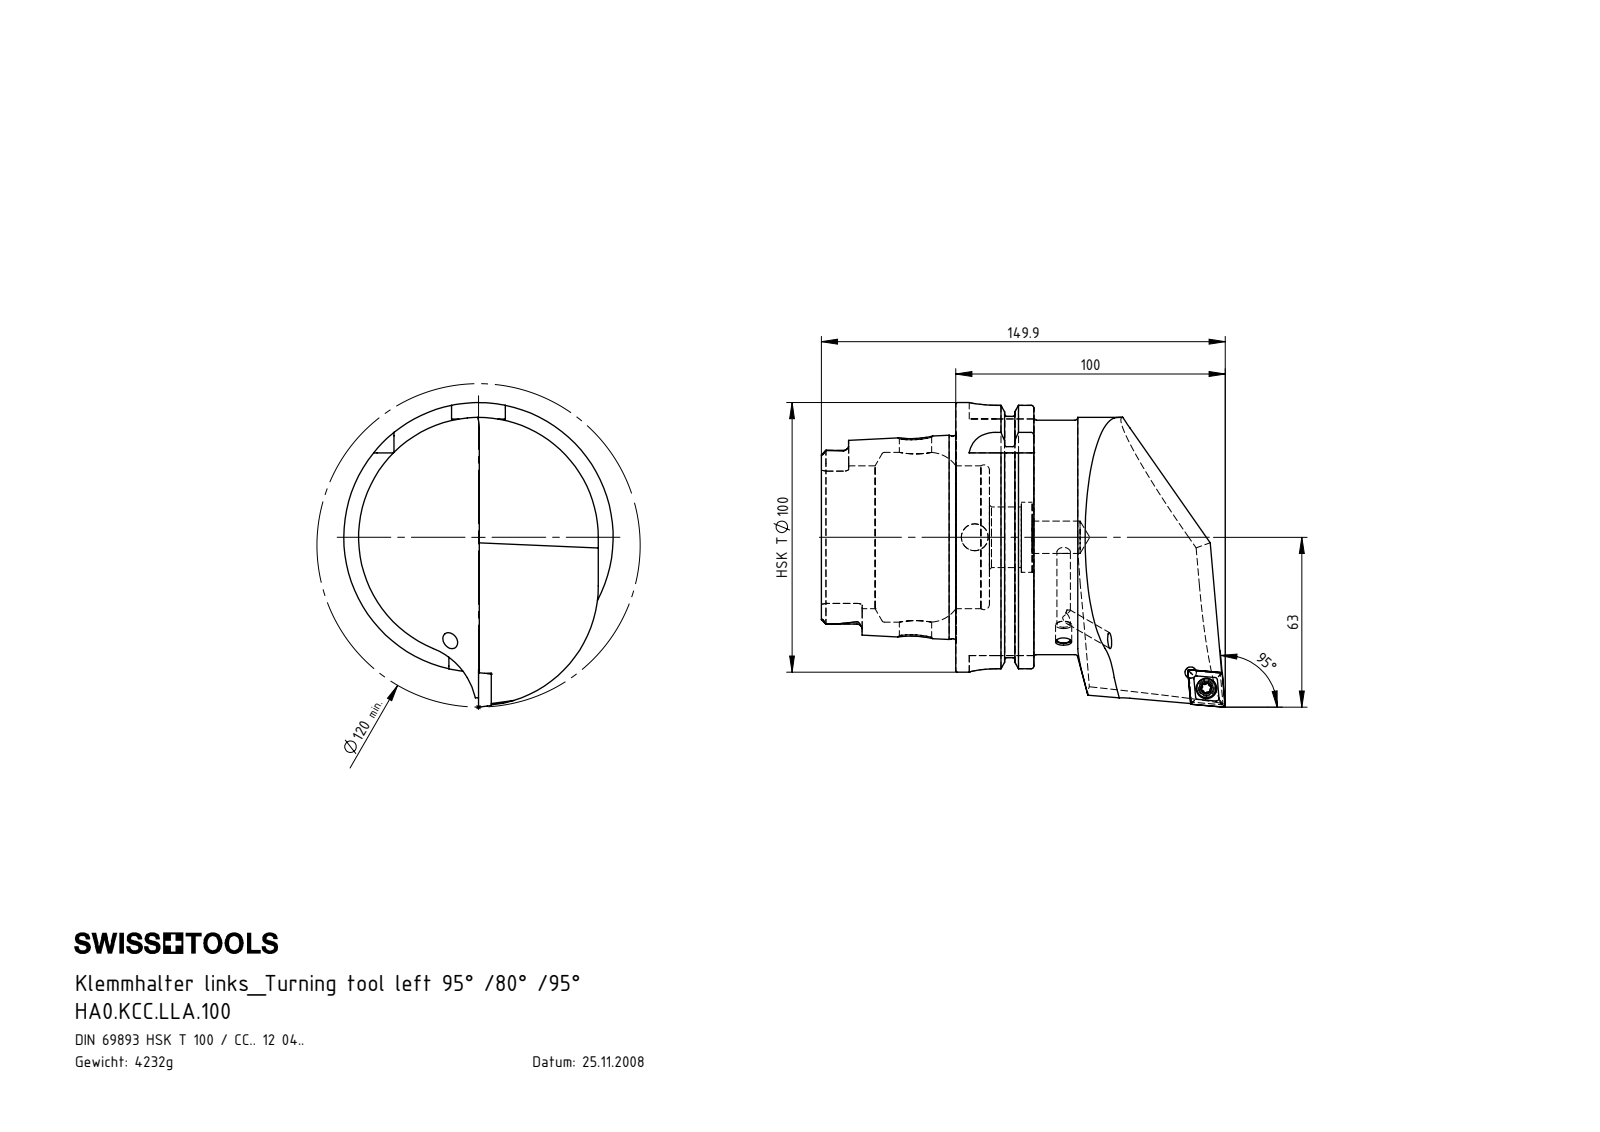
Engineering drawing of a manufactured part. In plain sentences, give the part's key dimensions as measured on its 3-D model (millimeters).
The part is named "HA0-KCC.LLA.100_C_Fertigbearbeitung; CCMT120404; KVT_MB_600_050; WCC-ER2.001.010_A (+1 more)". Its 3-D file was written by "SolidWorks 2009 (CONFIG_CONTROL_DESIGN)". It is 5 solids with 306 faces: 72 planar, 94 cylindrical and 140 other. Overall it measures 149.9 by 113 by 100 millimeters. Its volume is 532 852 cubic millimeters and its surface area 68 712 square millimeters. Round holes: 4 of diameter 4.2, 2 of diameter 12, 1 of diameter 4, 1 of diameter 5.5, 1 of diameter 7.6, 1 of diameter 10, 1 of diameter 22.5, 1 of diameter 26, 1 of diameter 53, 1 of diameter 63. Round bosses or shafts: 2 of diameter 5, 1 of diameter 100, 1 of diameter 91.95, 1 of diameter 87, 1 of diameter 75.26, 1 of diameter 7. Partial cylindrical surfaces (rounded edges, fillets, slot ends): 6 of radius 0.39, 6 of radius 1.9, 4 of radius 10, 3 of radius 0.69, 3 of radius 0.69, 2 of radius 4.83, 2 of radius 4.88, 1 of radius 6. The main face-to-face distances are 44.2, 12.45, 28.95, 16.5, 49.9, 62.35, 78.85, 87.8, 78.2, 28.3. The hole center spacings are 8.2, 8.32, 94.57, 102.58, 102.69.
